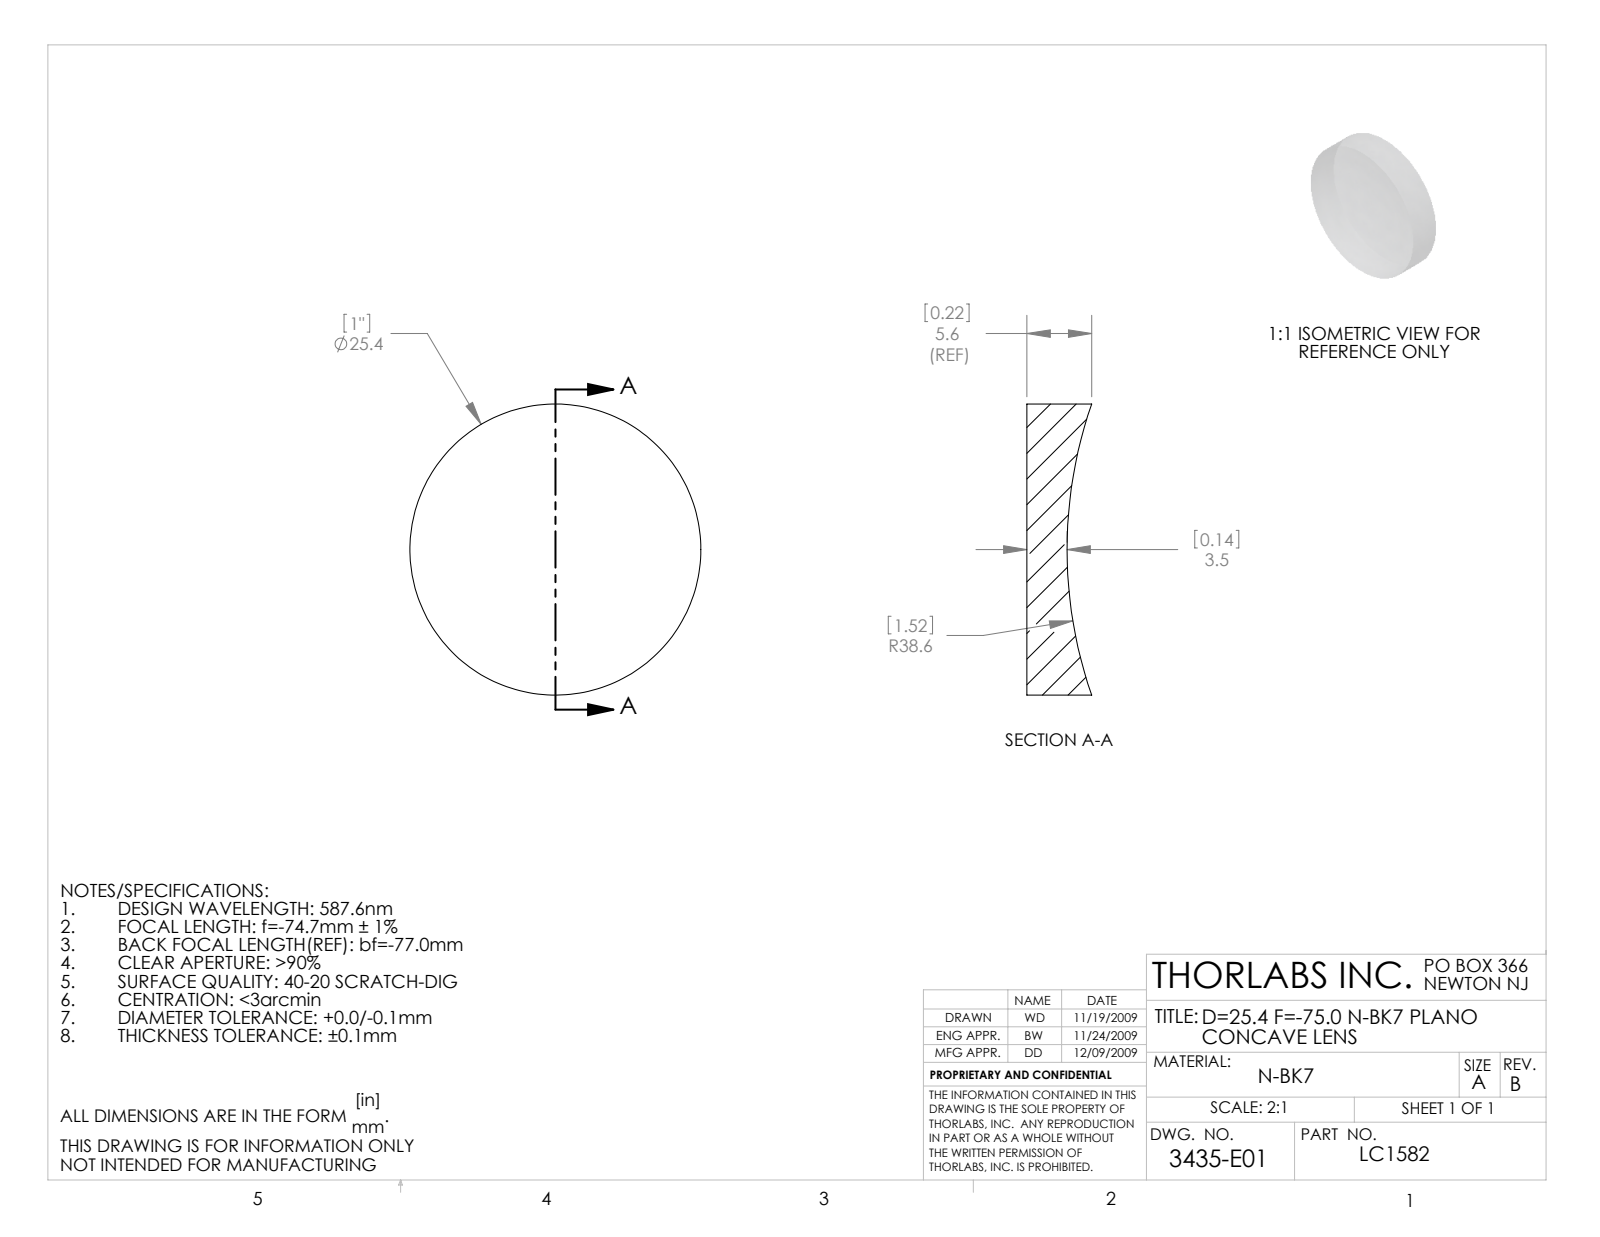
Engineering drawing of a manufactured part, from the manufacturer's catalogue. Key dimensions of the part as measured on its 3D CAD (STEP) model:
Part name (STEP PRODUCT): 3435-E0W
STEP written by: SolidWorks 2009 (AUTOMOTIVE_DESIGN)
Units: millimetres
Bodies: 1 solid, 5 faces (1 planar, 2 cylindrical, 2 other)
Overall size (bounding box): 25.4 × 25.4 × 5.65
Volume: 2 313 mm³ · Surface area: 1 479 mm²
Round bosses / shafts (diameter × count): ⌀25.4 ×1
